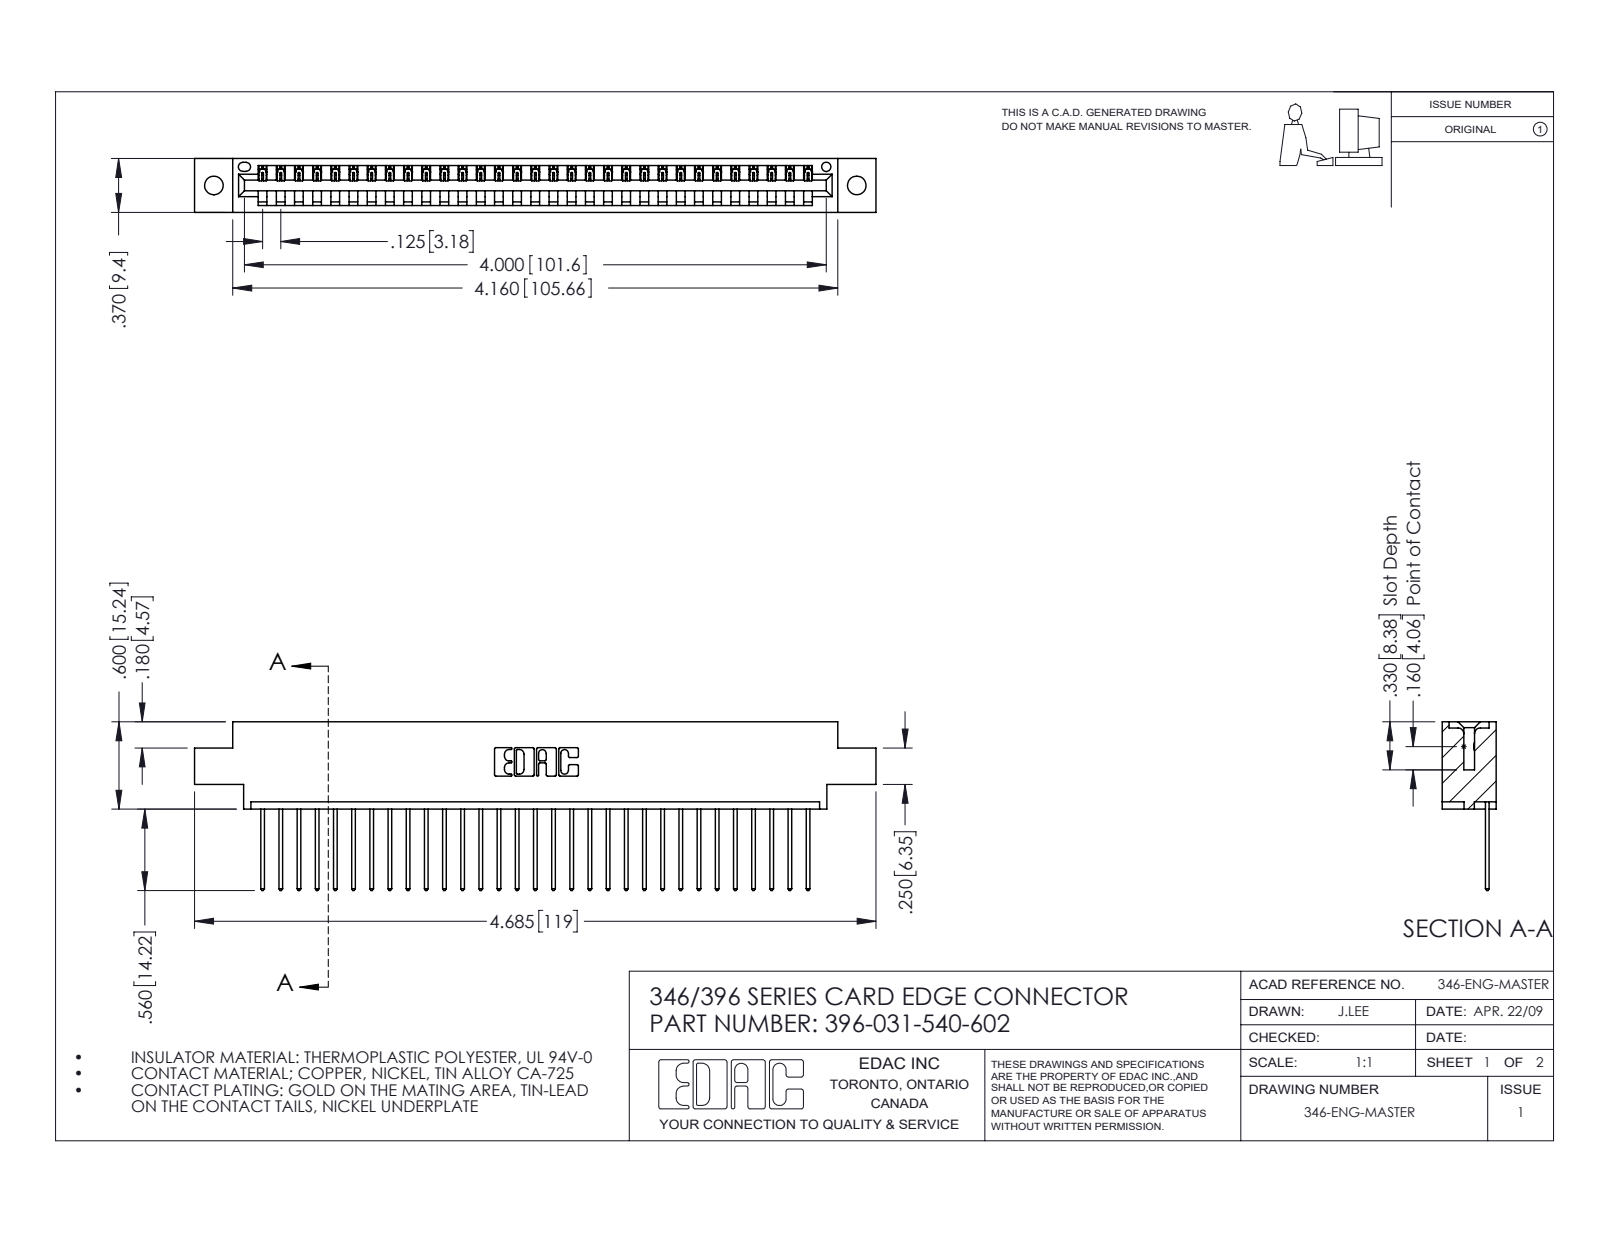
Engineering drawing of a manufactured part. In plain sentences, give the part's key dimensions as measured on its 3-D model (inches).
The part is named "346 Part_0.170 Offset - 0.128 Dia; 345-292-001_345-293-140; 396-031-540-602". Its 3-D file was written by "SolidWorks 2016 (CONFIG_CONTROL_DESIGN)". It is 32 solids with 1924 faces: 1320 planar, 604 cylindrical and 0 other. Overall it measures 4.685 by 1.16 by 0.37 inches. Its volume is 0.681 cubic inches and its surface area 21.75 square inches. Round holes: 2 of diameter 0.128, 1 of diameter 0.064. Partial cylindrical surfaces (rounded edges, fillets, slot ends): 62 of radius 0.006, 62 of radius 0.01, 22 of radius 0.01, 6 of radius 0.007, 6 of radius 0.031, 3 of radius 0.026, 2 of radius 0.031, 2 of radius 0.04. The main face-to-face distances are 0.048, 0.322, 0.37, 0.25, 0.072, 0.298, 0.025, 0.148, 0.222, 0.1. The hole center spacings are 0.246, 4.212, 4.42.
